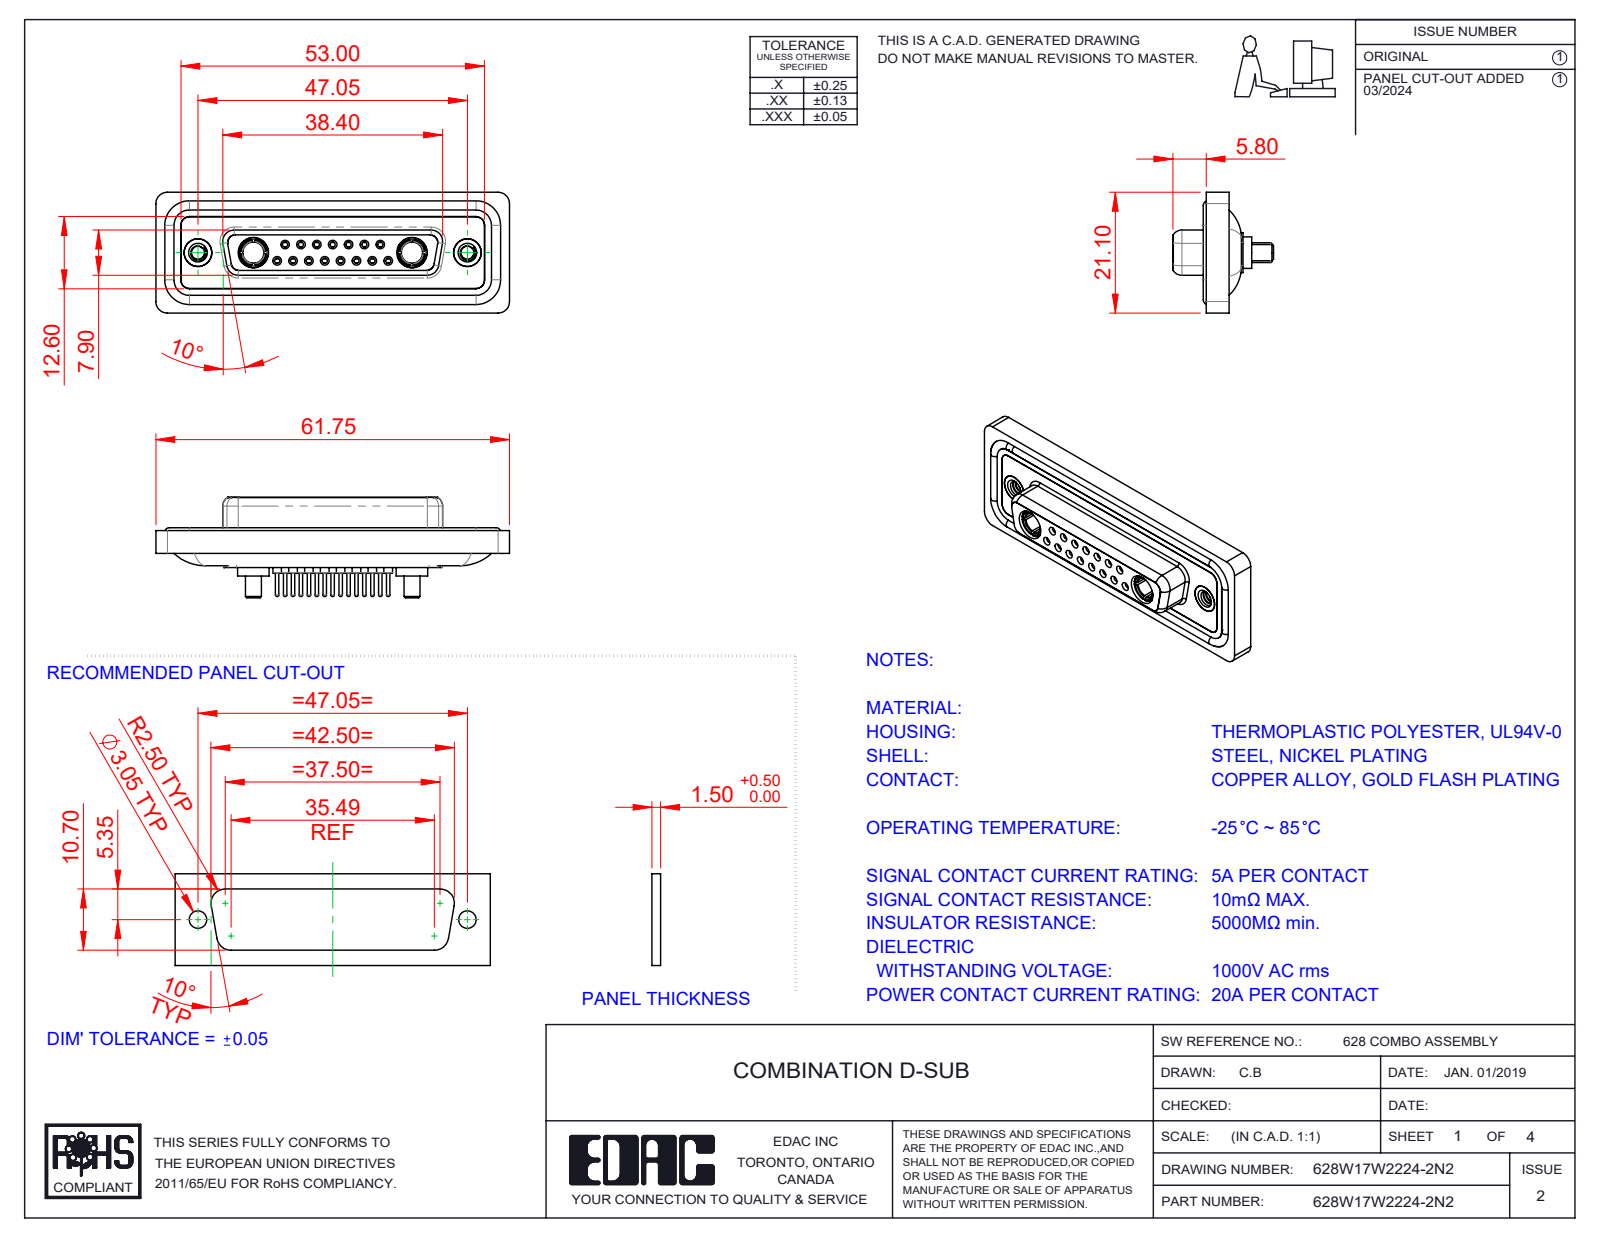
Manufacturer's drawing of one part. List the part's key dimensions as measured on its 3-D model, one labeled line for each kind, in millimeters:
Part name (STEP PRODUCT): 628W17W2224-2N2; 628Combo Housing_17W2; 628Combo Shell Front_25 Contacts; 628Combo Waterproof Housing_25 Contacts (+5 more)
STEP written by: SolidWorks 2023 (CONFIG_CONTROL_DESIGN)
Units: millimetres
Bodies: 26 solids, 1359 faces (388 planar, 519 cylindrical, 452 other)
Overall size (bounding box): 61.75 × 21.1 × 17.55
Volume: 8 324 mm³ · Surface area: 13 855 mm²
Round holes (diameter × count): ⌀0.9 ×15, ⌀1.1 ×15, ⌀1.5 ×15, ⌀2 ×15, ⌀1.6 ×8, ⌀1.7 ×7, ⌀4.85 ×4, ⌀2.26 ×2, ⌀3.7 ×2, ⌀4 ×2, ⌀4.05 ×2, ⌀5 ×2
Round bosses / shafts (diameter × count): ⌀2.2 ×15, ⌀0.6 ×15, ⌀1.6 ×11, ⌀5.5 ×2, ⌀5.2 ×2, ⌀4.96 ×2, ⌀4.95 ×2, ⌀4.8 ×2
Partial cylindrical surfaces — rounded edges, fillets, slot ends (radius × count): R1.5 ×22, R2 ×18, R1.35 ×8, R1.6 ×8, R0.25 ×4, R0.5 ×4, R0.6 ×4, R0.65 ×4
Main face-to-face distances: 0.4, 1.8, 7.45, 5.65, 6.6, 0.5, 7.05, 1.6, 2.9, 1.1
Hole centre spacings: 3.16, 2.77, 8.31, 5.54, 5.03, 5.04, 7.49, 11.08
